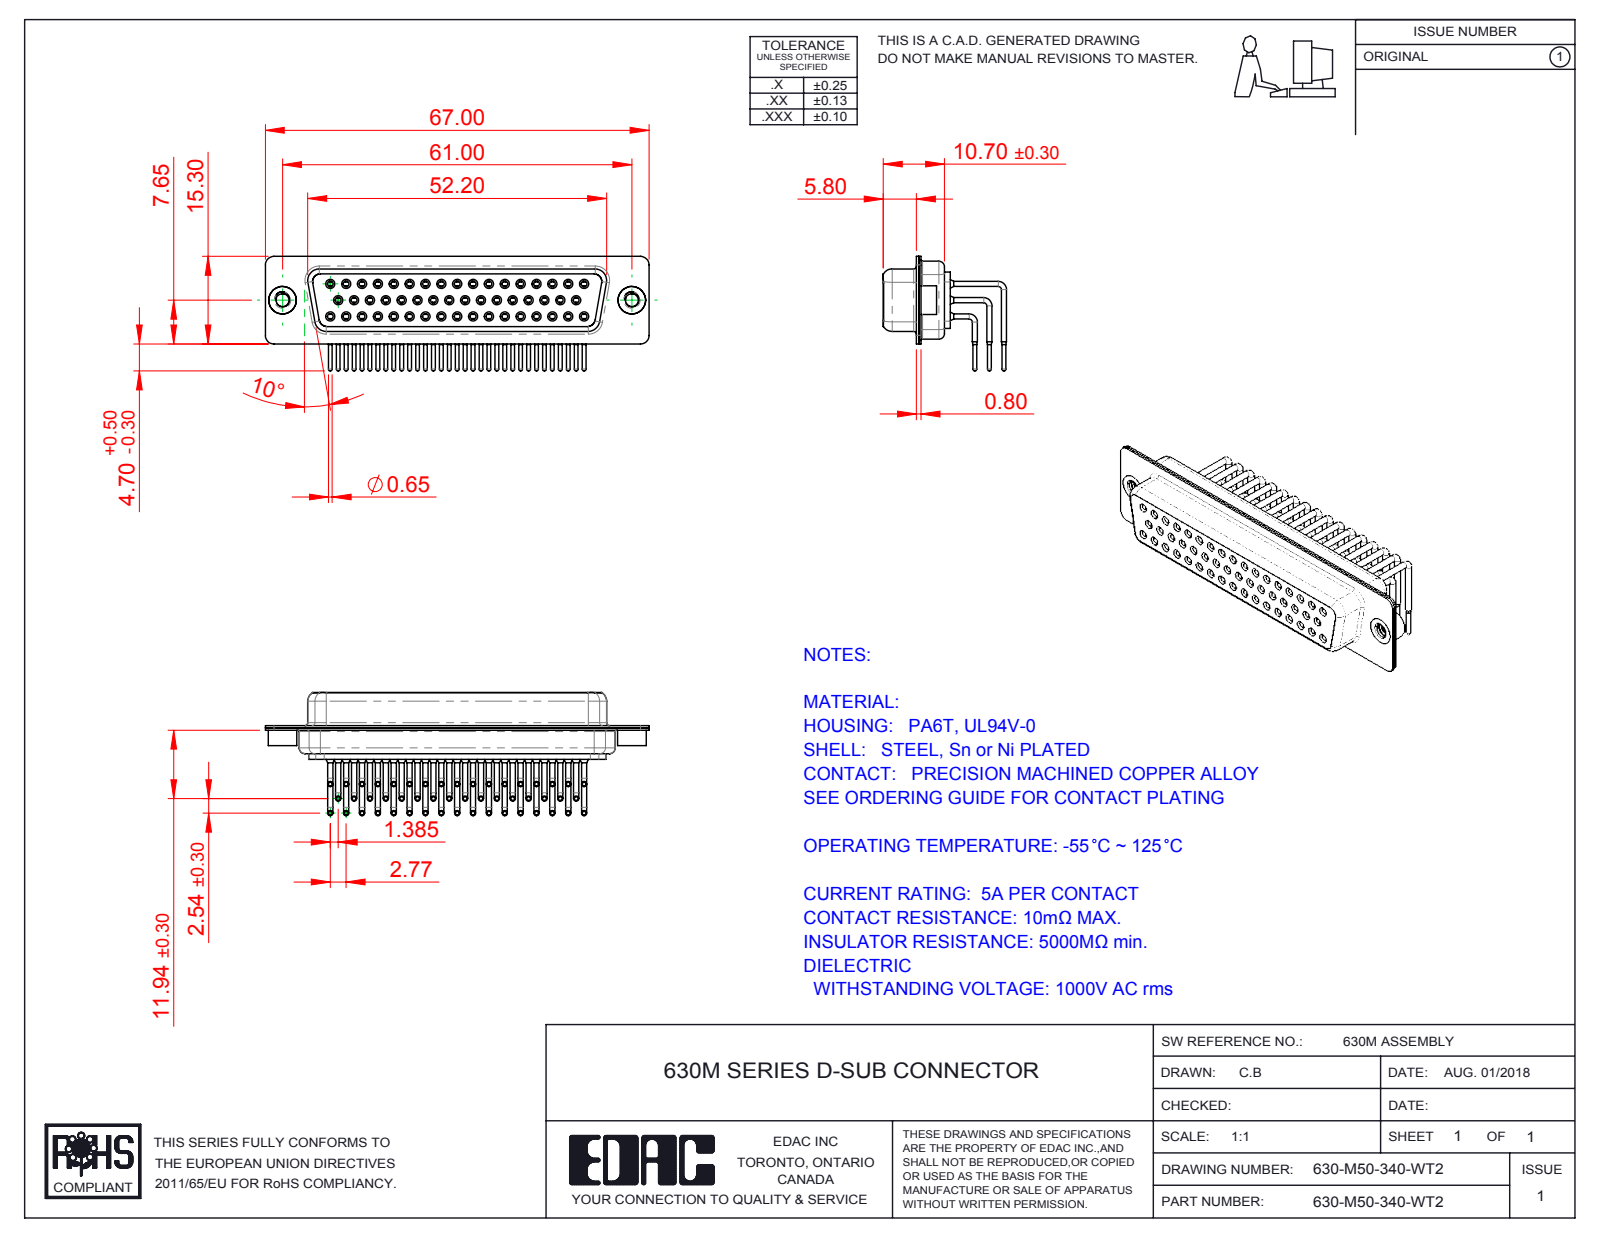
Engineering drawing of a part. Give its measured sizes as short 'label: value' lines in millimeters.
name: 630M Housing_50 Contacts; 630M Contact Row 2_50 Contacts; 630M Shell Front_50 Contacts; 630M 4-40 Threaded Rivet (+4 more)
written by: SolidWorks 2016 (CONFIG_CONTROL_DESIGN)
unit: mm
bodies: 55 solids, 2929 faces (817 planar, 1287 cylindrical, 825 other)
size: 67 × 21.53 × 20
volume: 7 020 mm³; area: 16 564 mm²
holes: 50× ⌀1, 50× ⌀1.1, 50× ⌀1.7, 50× ⌀1.8, 50× ⌀2, 2× ⌀2.26, 2× ⌀4, 2× ⌀4.8
bosses: 100× ⌀0.9, 50× ⌀1.6, 50× ⌀1.5, 50× ⌀0.65, 2× ⌀5, 2× ⌀4.9
rounds: 16× R1.5, 12× R2, 8× R1.35, 8× R1.6, 4× R0.25, 4× R0.5, 4× R0.6, 4× R0.65
face distances: 0.4, 1.35, 11.85, 0.85, 2.2, 5.5, 12.25, 5.9, 10.5, 0.8
hole spacings: 2.77, 3.16, 5.54, 8.31, 11.08, 13.85, 16.62, 19.39
